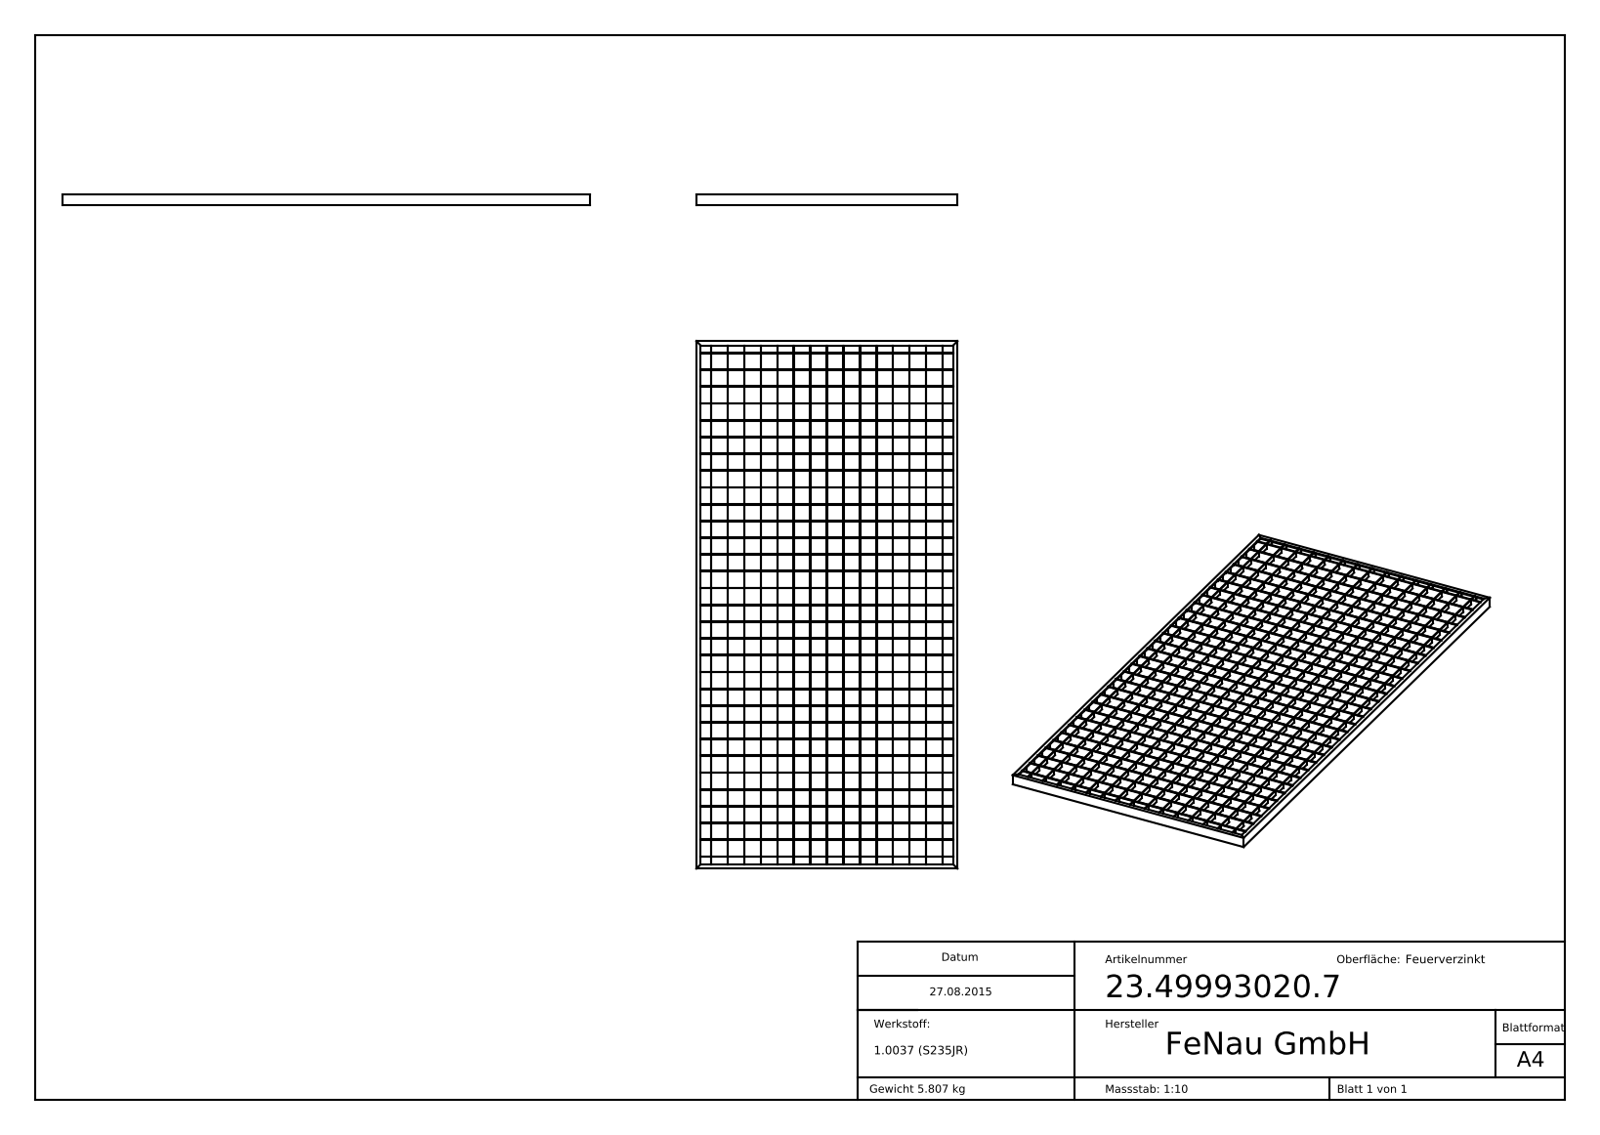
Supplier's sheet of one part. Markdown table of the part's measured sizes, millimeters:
| quantity | value |
| --- | --- |
| part name | 23-49993020-7 |
| STEP written by | SolidWorks 2015 (CONFIG_CONTROL_DESIGN) |
| units | millimeters |
| bodies | 1 solid, 1768 faces (1768 planar, 0 cylindrical, 0 other) |
| overall size | 990 × 490 × 20 |
| volume | 744 549 mm³ |
| surface area | 1 108 000 mm² |
| main face-to-face distances | 63, 31.5, 94.5, 31, 126, 157.5, 189, 62, 220.5, 252 |
